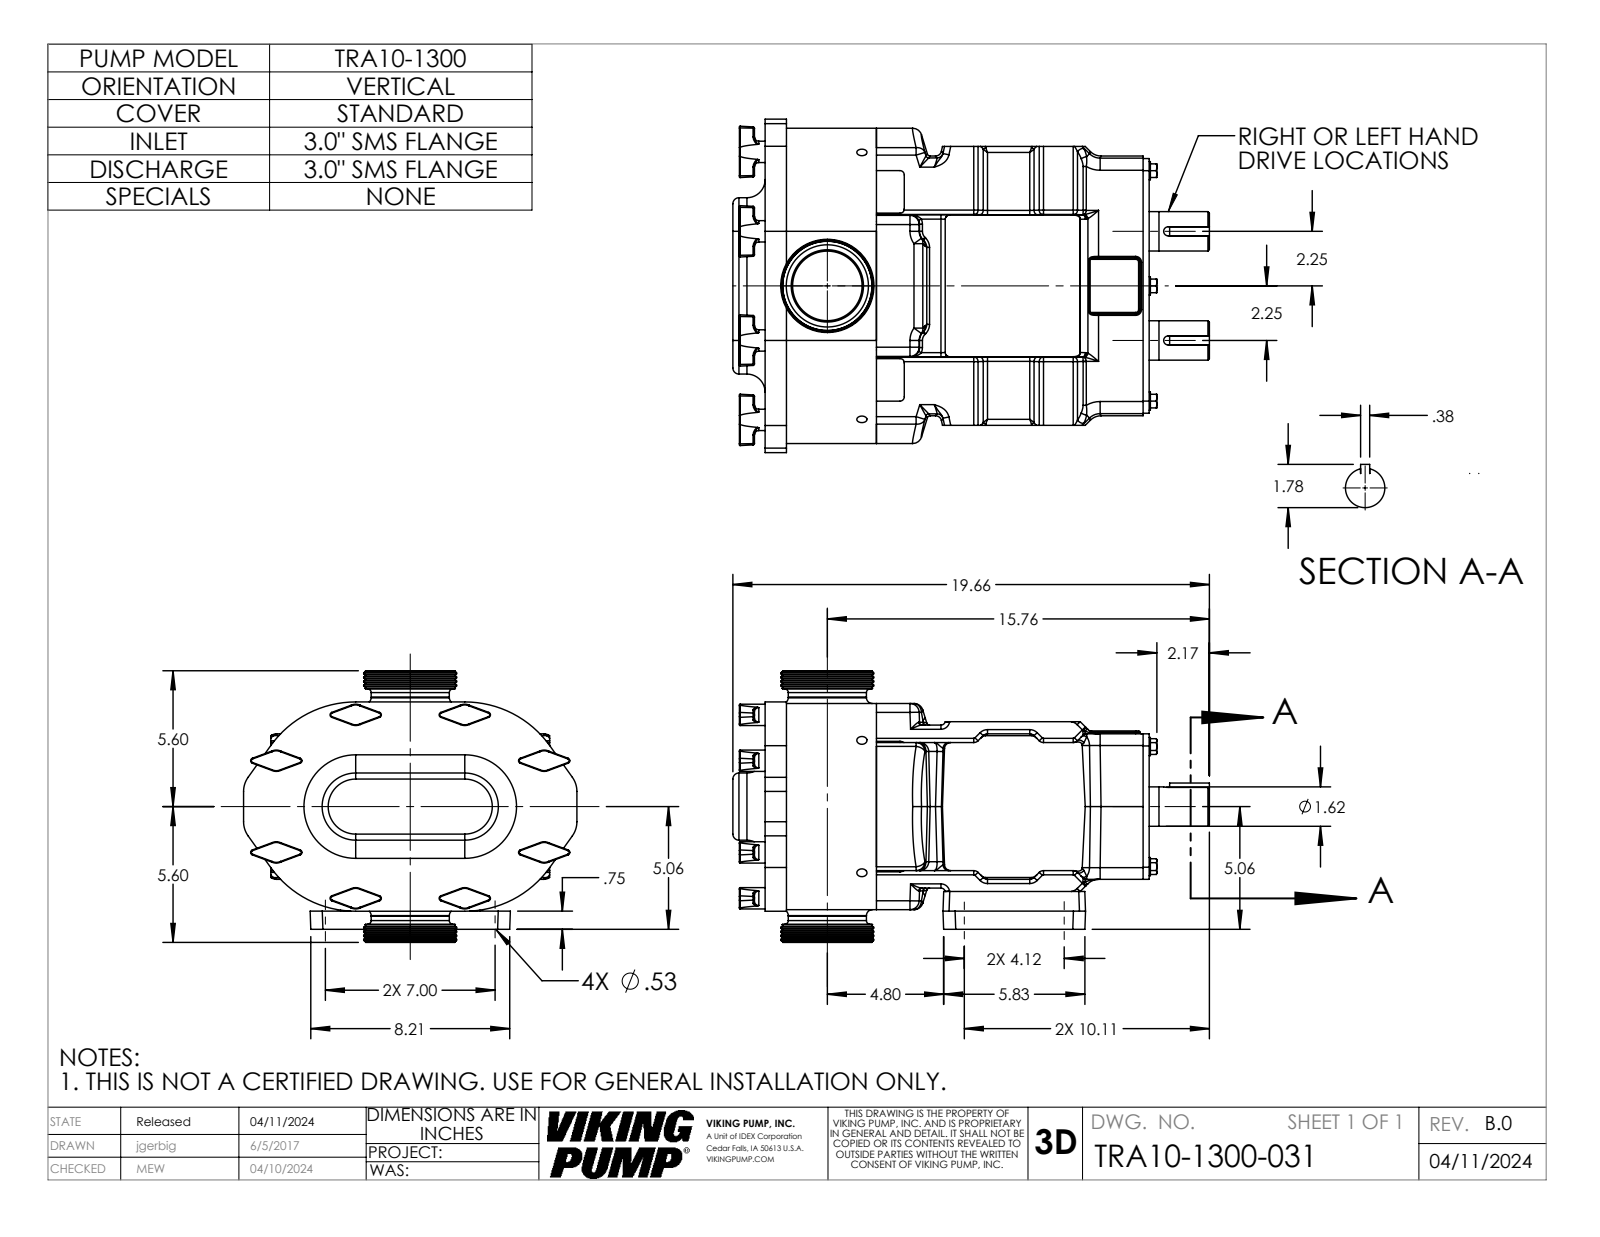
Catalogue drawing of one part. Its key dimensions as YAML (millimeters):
part_name: "TRA10-1300-031; TRA10-0600-COVER-STD; 1300SMS30; TRA10-0600-GEARBOX-V (+1 more)"
step_written_by: "SolidWorks 2022 (AUTOMOTIVE_DESIGN)"
units: millimeters
bodies: {solids: 5, faces: 1159, planar: 287, cylindrical: 384, other: 488}
overall_size: [499.3, 349.3, 284.5]
volume: 20960000
surface_area: 909000
round_holes:
  - {diameter: 8.4, count: 4}
  - {diameter: 13.5, count: 4}
  - {diameter: 72.8, count: 1}
  - {diameter: 86.1, count: 1}
round_bosses_or_shafts:
  - {diameter: 22.4, count: 8}
  - {diameter: 19.1, count: 6}
  - {diameter: 41.2, count: 2}
  - {diameter: 81.9, count: 1}
  - {diameter: 75.7, count: 1}
partial_cylinders:
  - {radius: 4.6, count: 44}
  - {radius: 1.5, count: 43}
  - {radius: 0.8, count: 32}
  - {radius: 6.4, count: 32}
  - {radius: 9.7, count: 28}
  - {radius: 3, count: 24}
  - {radius: 12.7, count: 20}
  - {radius: 9.5, count: 12}
face_to_face_distances: [94.3, 22.4, 116.6, 9.1, 402.4, 380, 285.8, 143.3, 12.7, 32.8]
hole_center_spacings: [73.5, 104.6, 168.8, 177.8, 206.3, 263.6]
